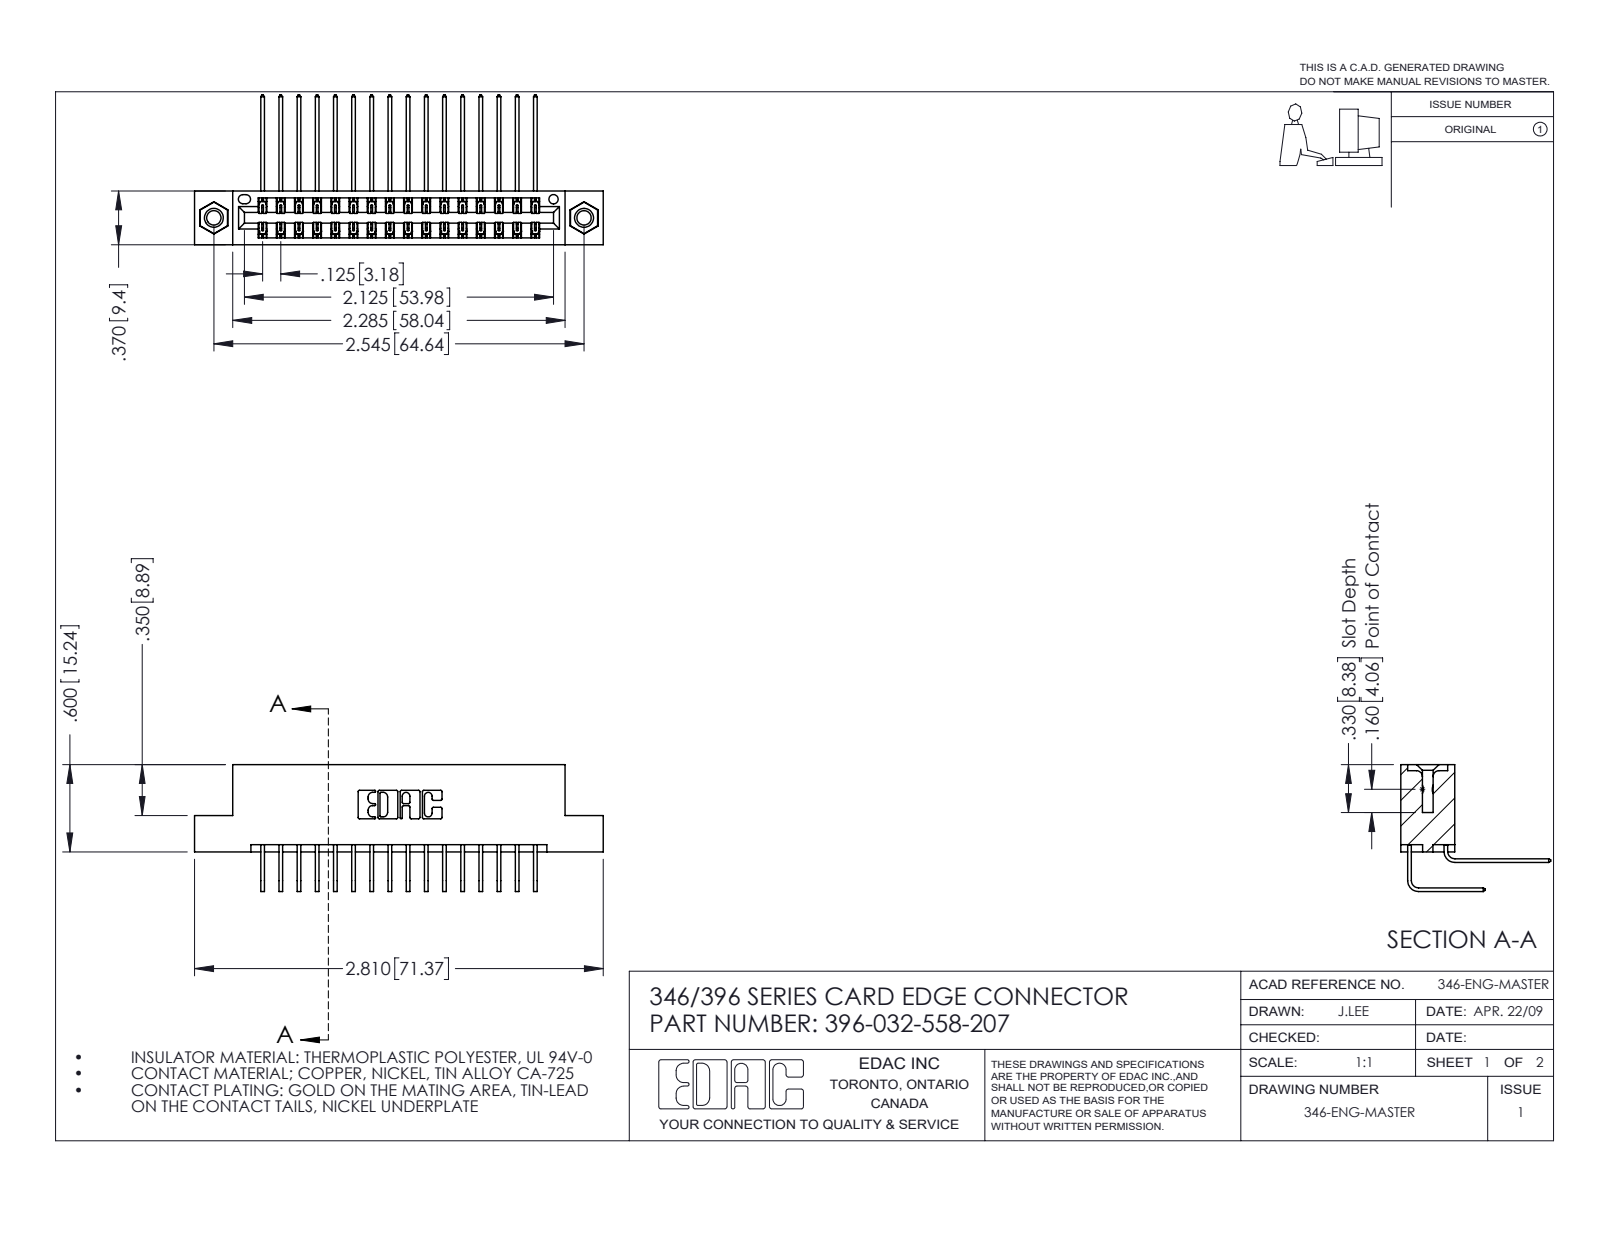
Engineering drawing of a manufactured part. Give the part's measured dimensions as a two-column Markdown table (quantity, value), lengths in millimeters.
| quantity | value |
| --- | --- |
| part name | 396-032-558-207; 345-250-001_345-250-005-103; 345-292-001_558 559 Tail - 1; 345-292-001_558 Tail - 2 (+1 more) |
| STEP written by | SolidWorks 2016 (CONFIG_CONTROL_DESIGN) |
| units | millimeters |
| bodies | 35 solids, 1910 faces (1292 planar, 602 cylindrical, 16 other) |
| overall size | 71.4 × 26.2 × 22.2 |
| volume | 6 930 mm³ |
| surface area | 10 030 mm² |
| round holes (diameter × count) | 2.5 × 2, 3.2 × 2, 4 × 2, 1.6 × 1 |
| round bosses / shafts (diameter × count) | 3.9 × 2 |
| partial cylindrical surfaces (radius × count) | 0.2 × 48, 0.3 × 22, 0.2 × 6, 0.8 × 6, 0.7 × 3, 0.4 × 2, 0.6 × 2, 0.6 × 2 |
| main face-to-face distances | 8.2, 1.2, 6.4, 0.6, 9.4, 7.6, 1.8, 7, 3.8, 5.6 |
| hole center spacings | 6.2, 59.4, 64.6 |
